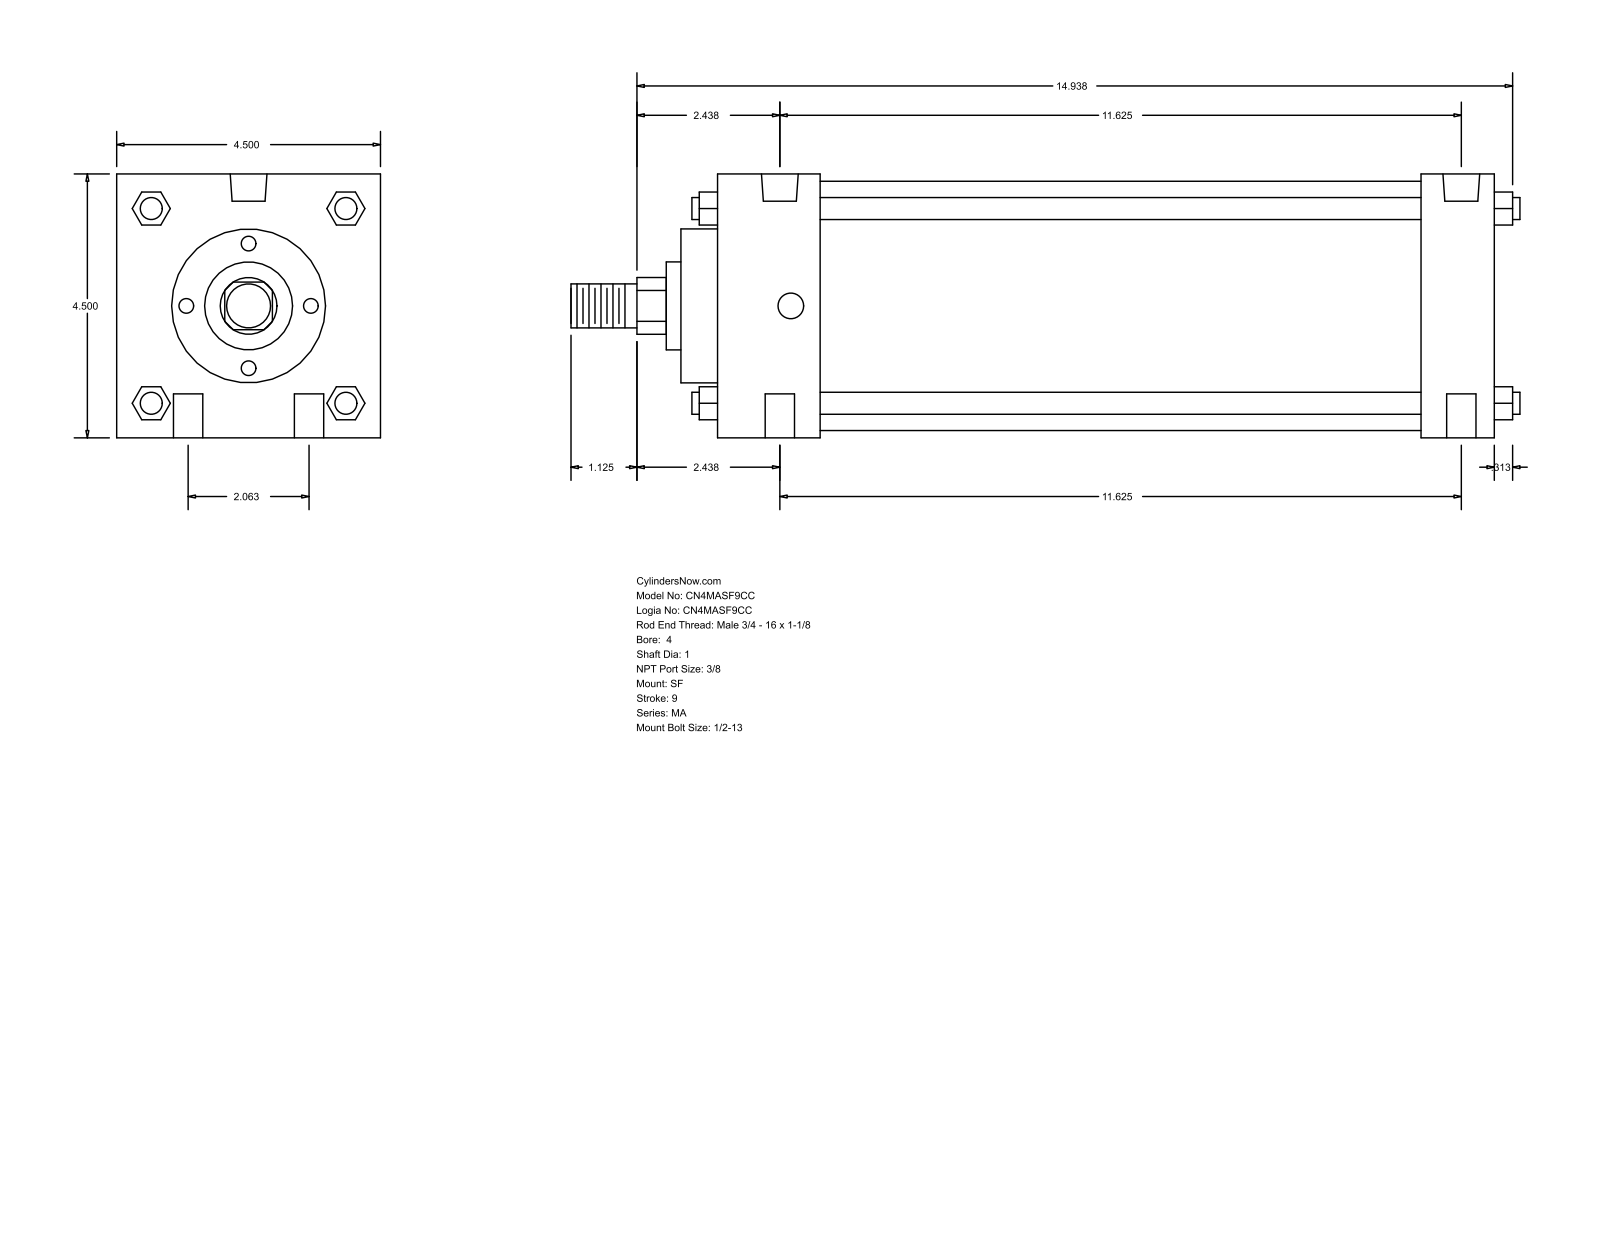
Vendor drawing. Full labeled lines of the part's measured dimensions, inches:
Part name (STEP PRODUCT): MA_SF__0400_1
STEP written by: GSSL Pune (CONFIG_CONTROL_DESIGN)
Units: inches
Bodies: 0 solids, 126 faces (95 planar, 31 cylindrical, 0 other)
Overall size (bounding box): 16.187 × 4.5 × 4.5
Round holes (diameter × count): ⌀0.5 ×4, ⌀0.437 ×2, ⌀0.627 ×2
Round bosses / shafts (diameter × count): ⌀0.375 ×4, ⌀4.25 ×1, ⌀2.625 ×1, ⌀1.5 ×1, ⌀1 ×1, ⌀0.75 ×1
Partial cylindrical surfaces — rounded edges, fillets, slot ends (radius × count): R0.484 ×1
Main face-to-face distances: 4.5, 13.25, 12, 1.25, 1.75, 10.25, 11.5, 0.625, 2.375, 12.625
Hole centre spacings: 1.031, 11.671, 11.625, 2.062, 11.807, 11.25
